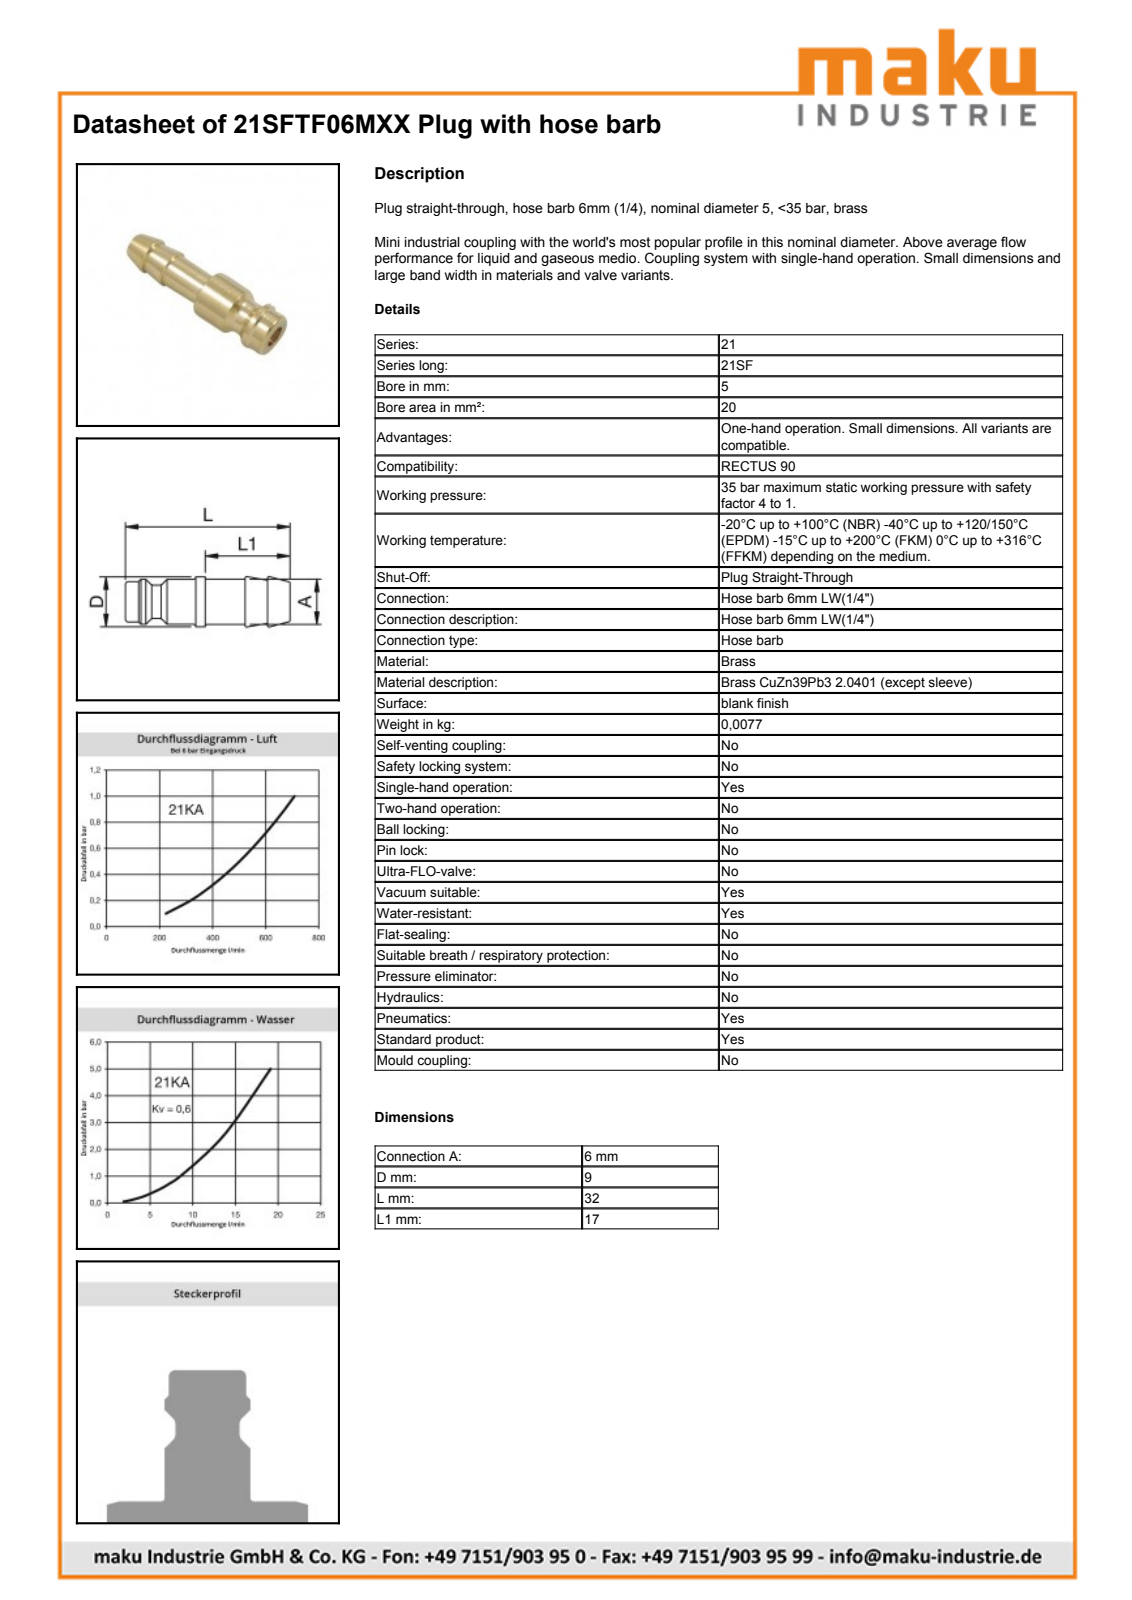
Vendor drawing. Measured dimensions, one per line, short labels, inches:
name: D107819
written by: Autodesk Inventor 2013 (AUTOMOTIVE_DESIGN)
unit: in
bodies: 1 solid, 24 faces (5 planar, 6 cylindrical, 13 other)
size: 1.26 × 0.354 × 0.354
volume: 0.057 in³; area: 1.919 in²
holes: 1× ⌀0.157
bosses: 1× ⌀0.354, 1× ⌀0.319, 1× ⌀0.262, 1× ⌀0.238
face distances: 0.591, 1.083, 0.492, 0.177, 0.906, 0.315, 1.26, 0.669, 0.354
